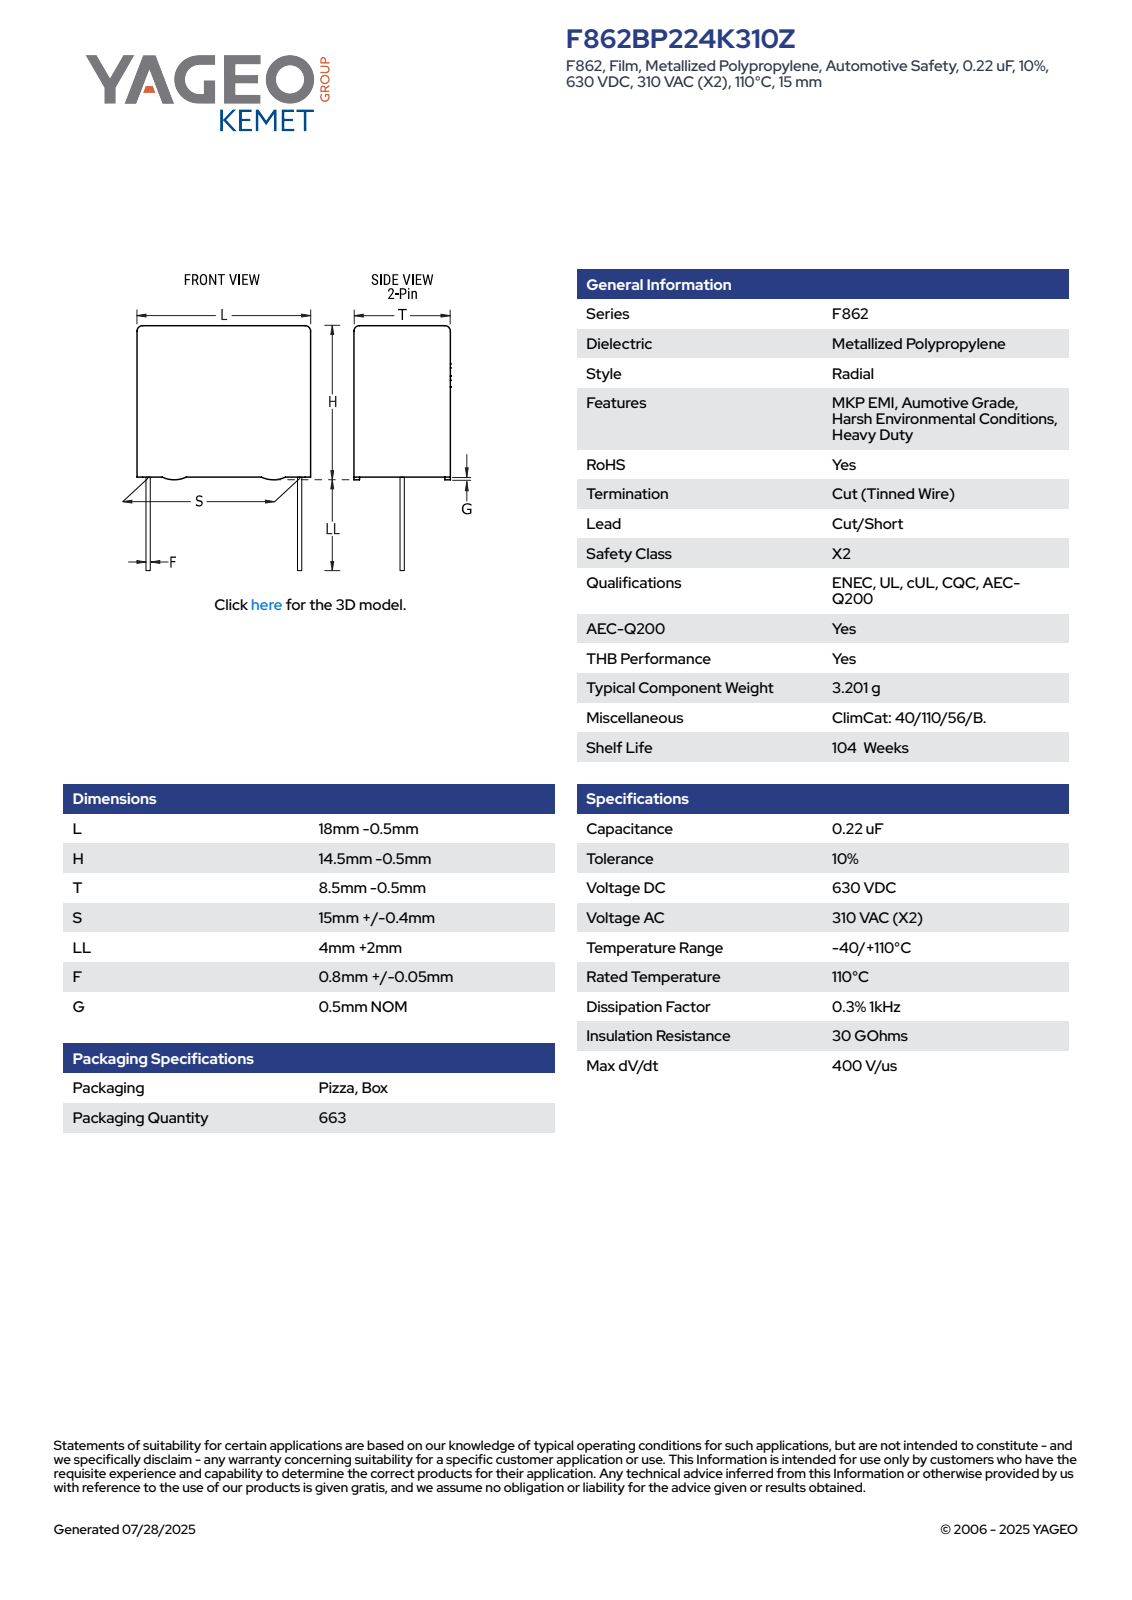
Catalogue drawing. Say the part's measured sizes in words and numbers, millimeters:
The part is named "CFR_RBG_18X14.5X8.5_L17.5H14T8S15LL6F0.85G0.5". Its 3-D file was written by "SolidWorks 2014 (AUTOMOTIVE_DESIGN)". It is 4 solids with 89 faces: 81 planar, 8 cylindrical and 0 other. Overall it measures 20 by 17.5 by 8.01 millimeters. Its volume is 1 897 cubic millimeters and its surface area 1 038 square millimeters. Round bosses or shafts: 2 of diameter 0.85. Partial cylindrical surfaces (rounded edges, fillets, slot ends): 4 of radius 0.5. The main face-to-face distances are 8, 13.5, 17.5, 8.01, 0.46, 7.54, 0.5, 14, 0.47, 7.08.
